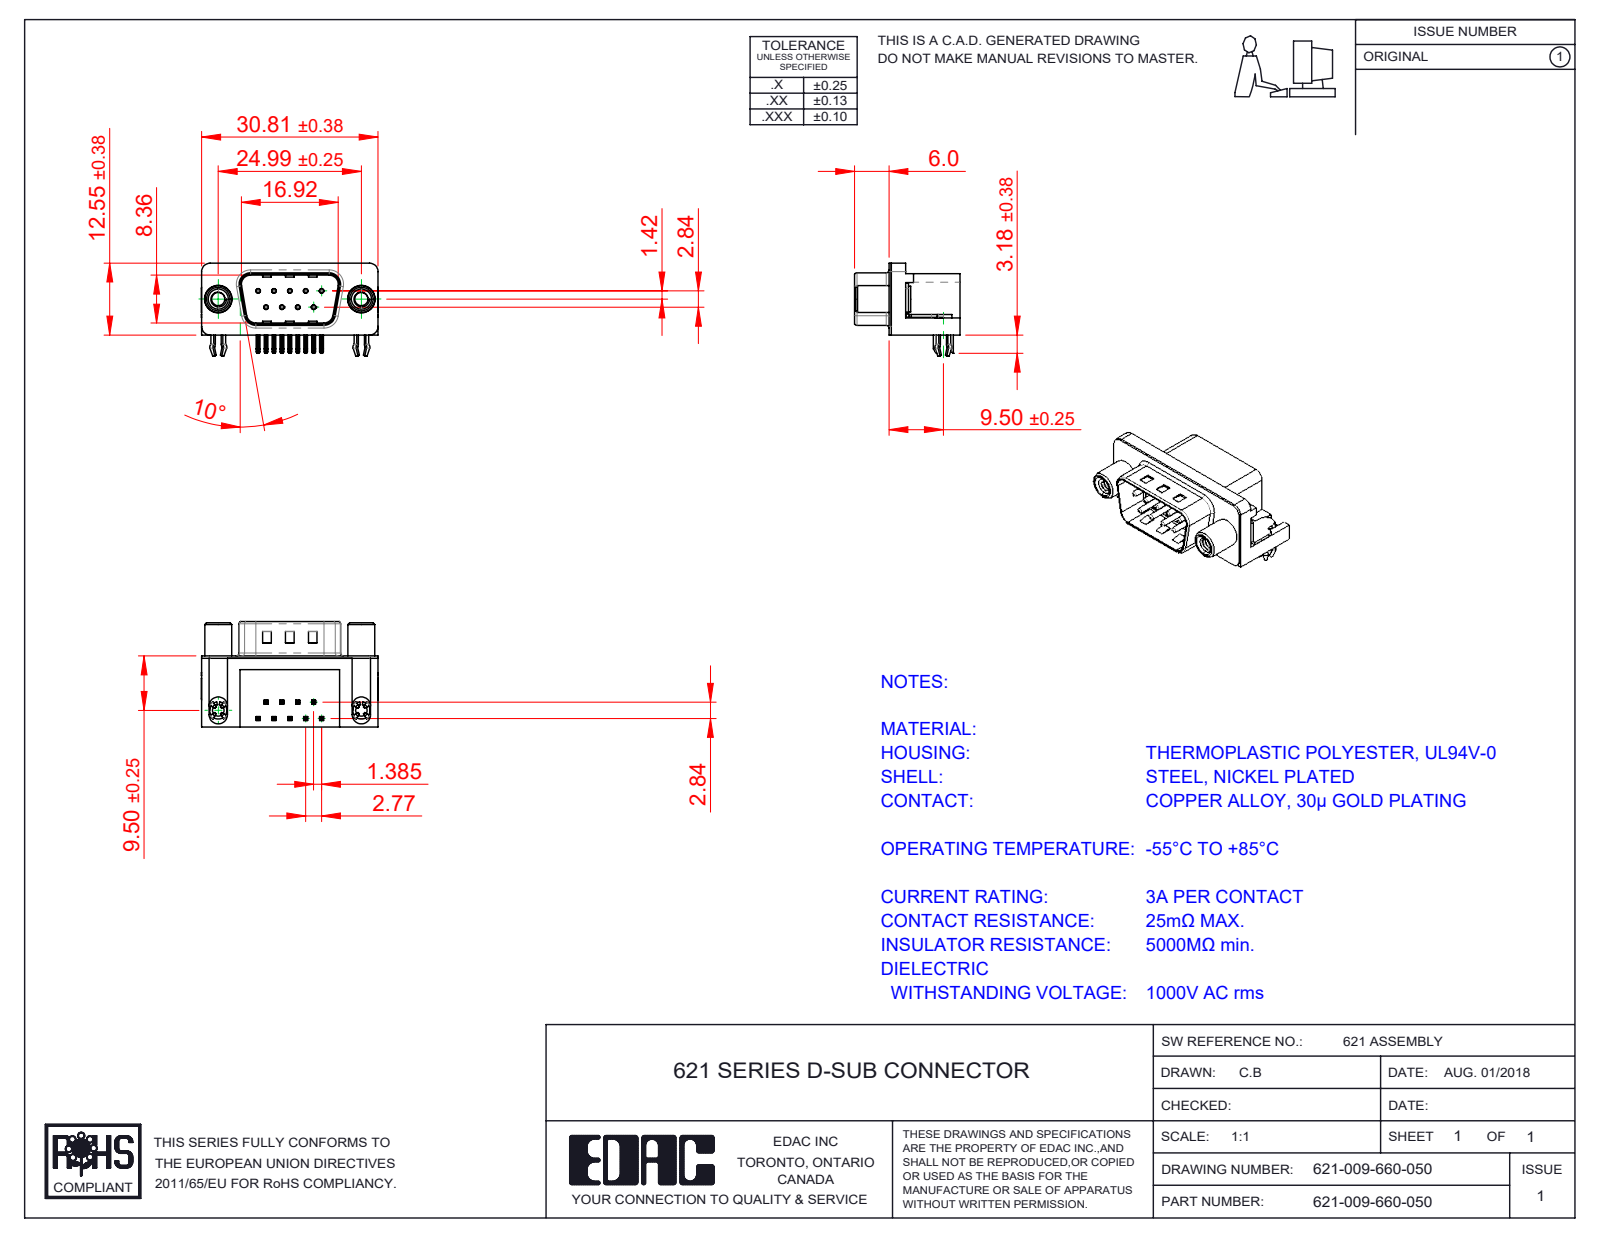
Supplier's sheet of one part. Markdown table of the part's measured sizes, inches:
| quantity | value |
| --- | --- |
| part name | 621 Contact Top; 621 Contact Bottom; 621-009-660-050; 621 Shell_9 Socket (+3 more) |
| STEP written by | SolidWorks 2016 (CONFIG_CONTROL_DESIGN) |
| units | inches |
| bodies | 15 solids, 1015 faces (565 planar, 335 cylindrical, 115 other) |
| overall size | 1.216 × 0.724 × 0.619 |
| volume | 0.204 in³ |
| surface area | 7.283 in² |
| round holes (diameter × count) | 0.014 × 9, 0.031 × 9, 0.089 × 2, 0.091 × 2, 0.122 × 2, 0.157 × 2, 0.189 × 2, 0.197 × 2 |
| round bosses / shafts (diameter × count) | 0.03 × 9, 0.193 × 2, 0.185 × 2, 0.177 × 2, 0.152 × 2, 0.128 × 2 |
| partial cylindrical surfaces (radius × count) | 0.01 × 36, 0.005 × 18, 0.039 × 16, 0.02 × 9, 0.059 × 8, 0.063 × 8, 0.035 × 4, 0.079 × 4 |
| main face-to-face distances | 0.016, 0.472, 0.488, 0.407, 0.098, 0.114, 0.374, 0.083, 0.02, 0.014 |
| hole center spacings | 0.124, 0.109, 0.218, 0.198, 0.198, 0.327, 0.294, 0.295 |
